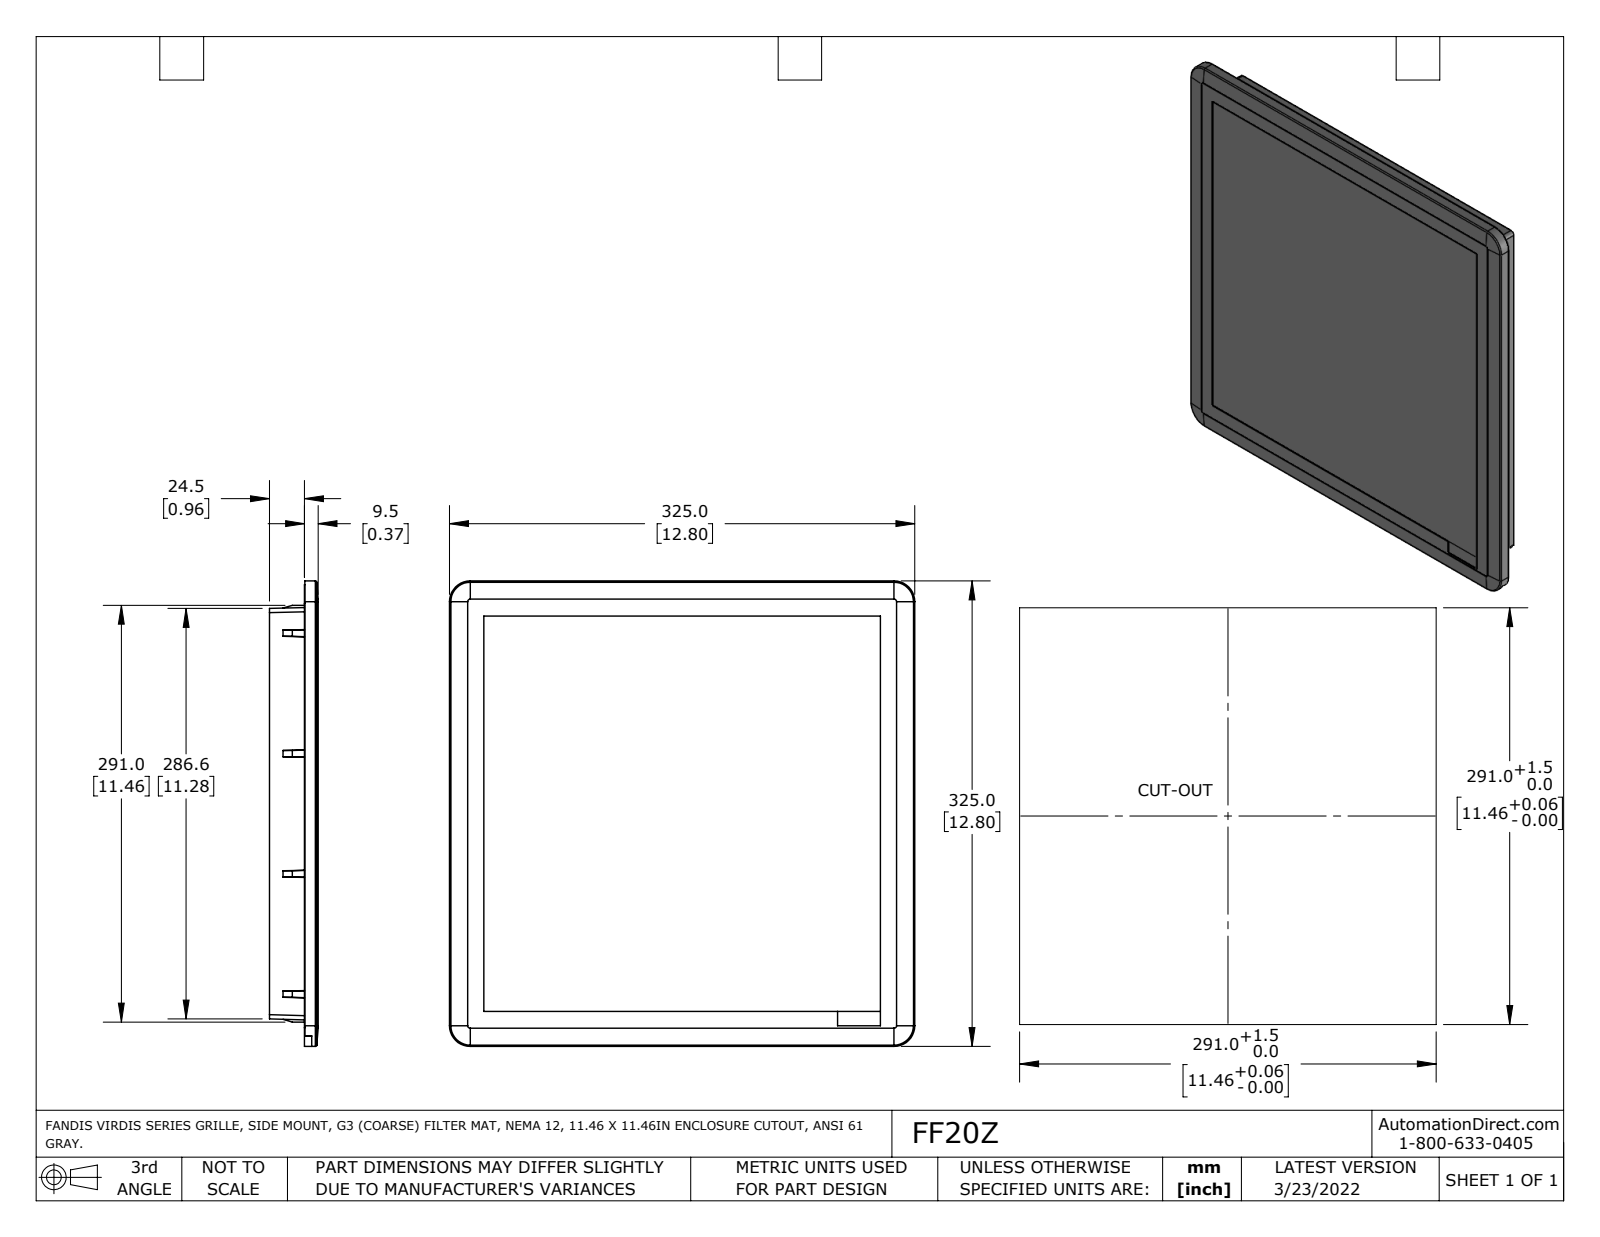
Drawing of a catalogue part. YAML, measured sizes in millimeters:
part_name: "FF20y (p.c.)"
step_written_by: "SolidWorks 2021 (AUTOMOTIVE_DESIGN)"
units: millimeters
bodies: {solids: 1, faces: 309, planar: 245, cylindrical: 44, other: 20}
overall_size: [325, 325, 34]
volume: 2984000
surface_area: 262100
partial_cylinders:
  - {radius: 1.2, count: 8}
  - {radius: 1, count: 4}
  - {radius: 3, count: 4}
  - {radius: 13, count: 4}
  - {radius: 14.5, count: 4}
  - {radius: 0.3, count: 2}
  - {radius: 12.5, count: 2}
face_to_face_distances: [33.7, 24.5, 9.2, 9.5, 34, 2.6, 322.4, 325, 2.4, 322.6]
